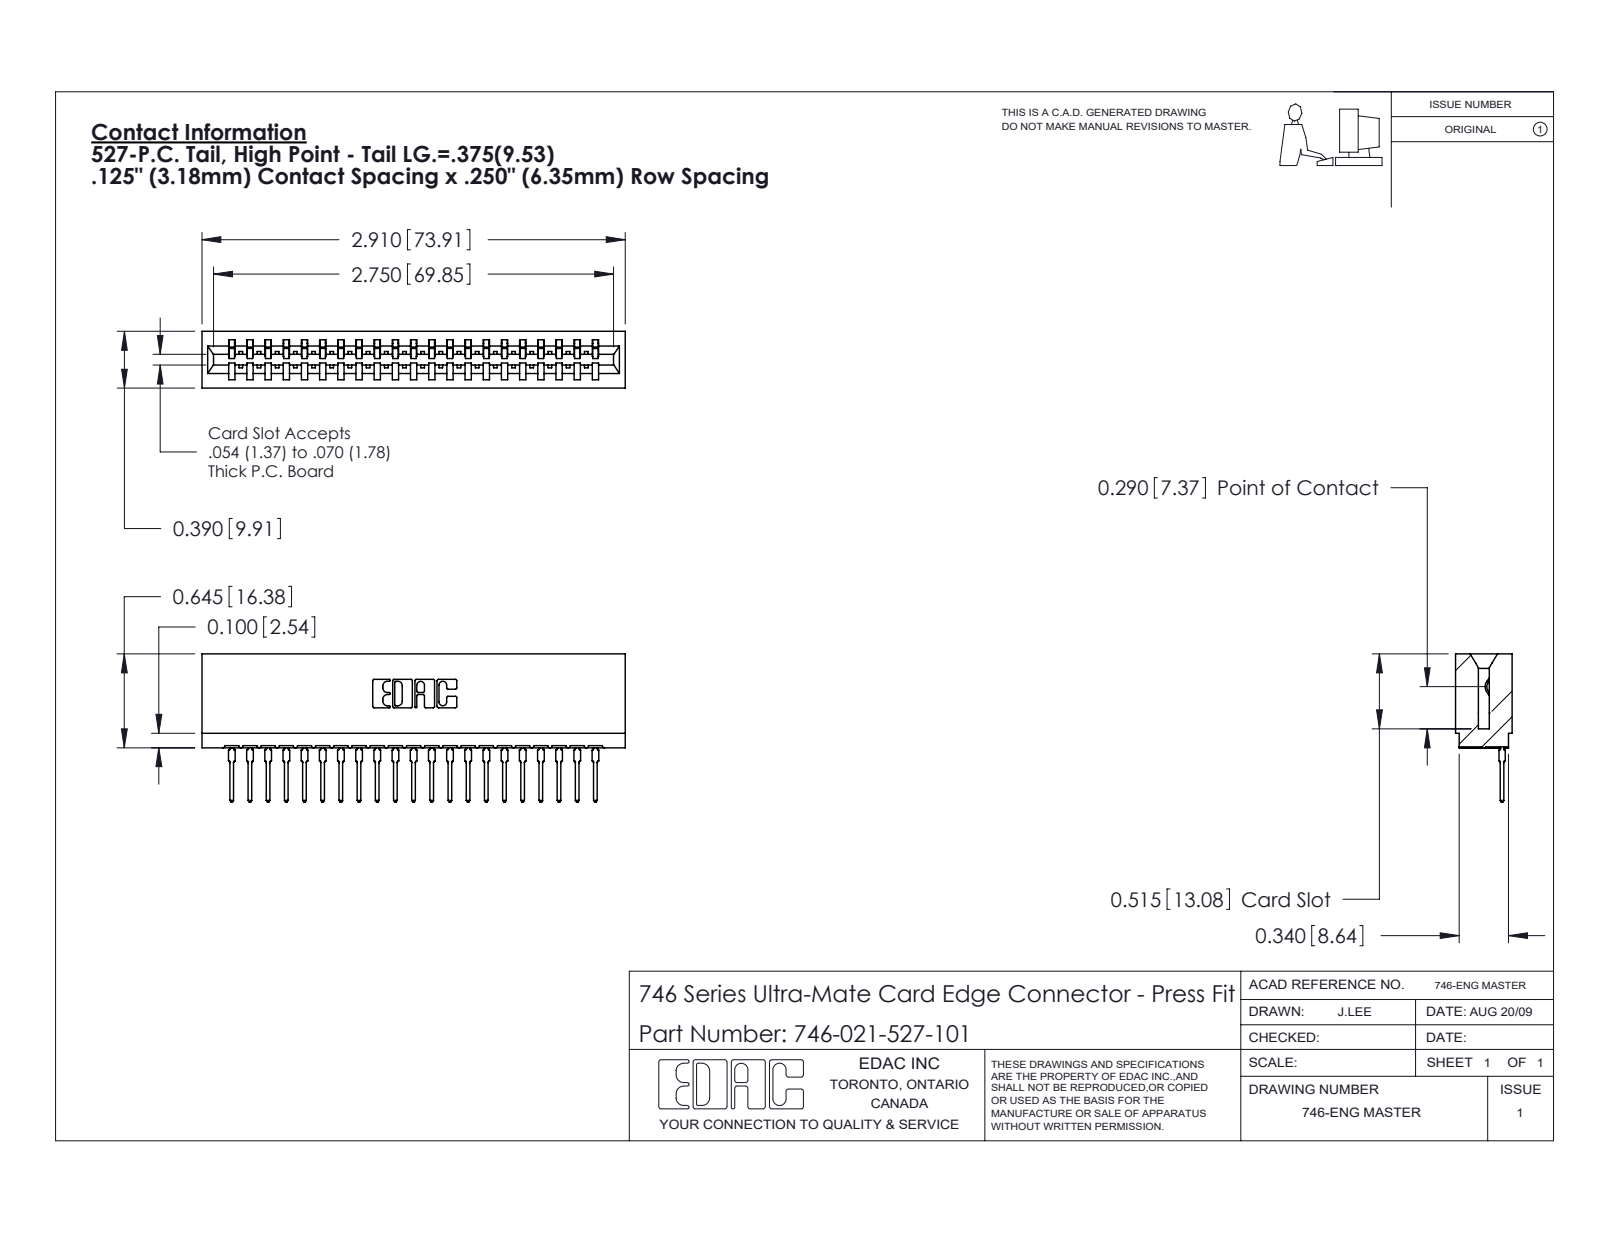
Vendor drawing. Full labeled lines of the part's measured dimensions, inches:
Part name (STEP PRODUCT): 746-021-527-101; 746 Part_.515 Slot Depth - 01; 746-292-001_527
STEP written by: SolidWorks 2020 (CONFIG_CONTROL_DESIGN)
Units: inches
Bodies: 22 solids, 2365 faces (1378 planar, 441 cylindrical, 546 other)
Overall size (bounding box): 2.91 × 1.019 × 0.39
Volume: 0.481 in³ · Surface area: 17.76 in²
Partial cylindrical surfaces — rounded edges, fillets, slot ends (radius × count): R0.021 ×42, R0.01 ×22, R0.015 ×22, R0.007 ×6, R0.031 ×6, R0.005 ×4, R0.011 ×4, R0.026 ×3
Main face-to-face distances: 0.25, 0.333, 0.057, 0.39, 0.5, 0.025, 0.307, 0.042, 0.125, 0.375
